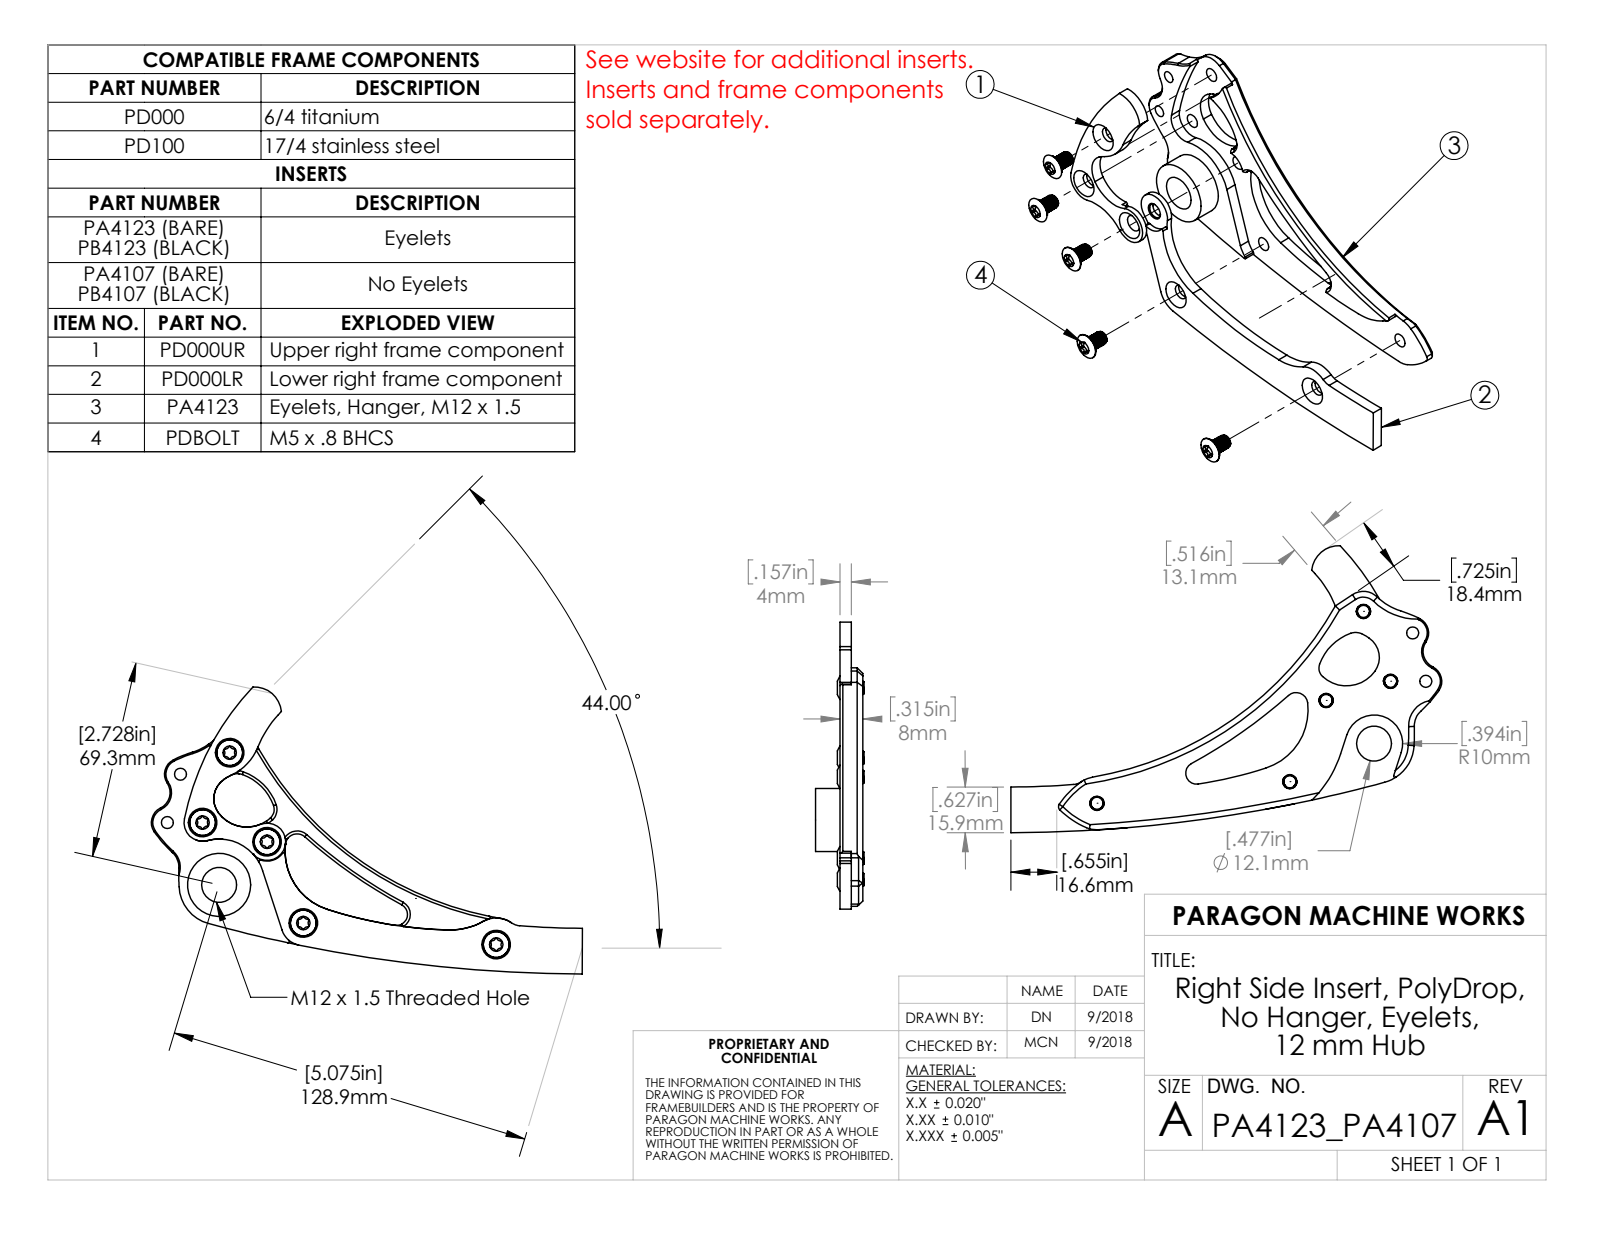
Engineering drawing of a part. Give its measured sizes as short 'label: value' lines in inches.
name: PA4123; M5x8OHCS_90258A246; Part2^PA4123_PA4107; Part1^PA4123_PA4107 (+3 more)
written by: SolidWorks 2018 (AUTOMOTIVE_DESIGN)
unit: in
bodies: 8 solids, 600 faces (30 planar, 326 cylindrical, 244 other)
size: 5.926 × 3.944 × 0.665
volume: 2.045 in³; area: 33.28 in²
holes: 5× ⌀0.209, 2× ⌀0.165, 2× ⌀0.197, 1× ⌀0.48
bosses: 30× ⌀0.171, 5× ⌀0.197, 1× ⌀0.866, 1× ⌀0.512
rounds: 30× R0.011, 30× R0.061, 14× R0.02, 5× R0.085, 2× R0.22, 2× R0.236, 2× R0.256, 2× R0.276
face distances: 0.157, 0.315, 0.079, 0.138, 0.02, 0.177, 0.65, 0.512, 0.492, 0.335
hole spacings: 0.886, 0.925, 1.223, 1.396, 1.51, 1.956, 2.669, 3.453
